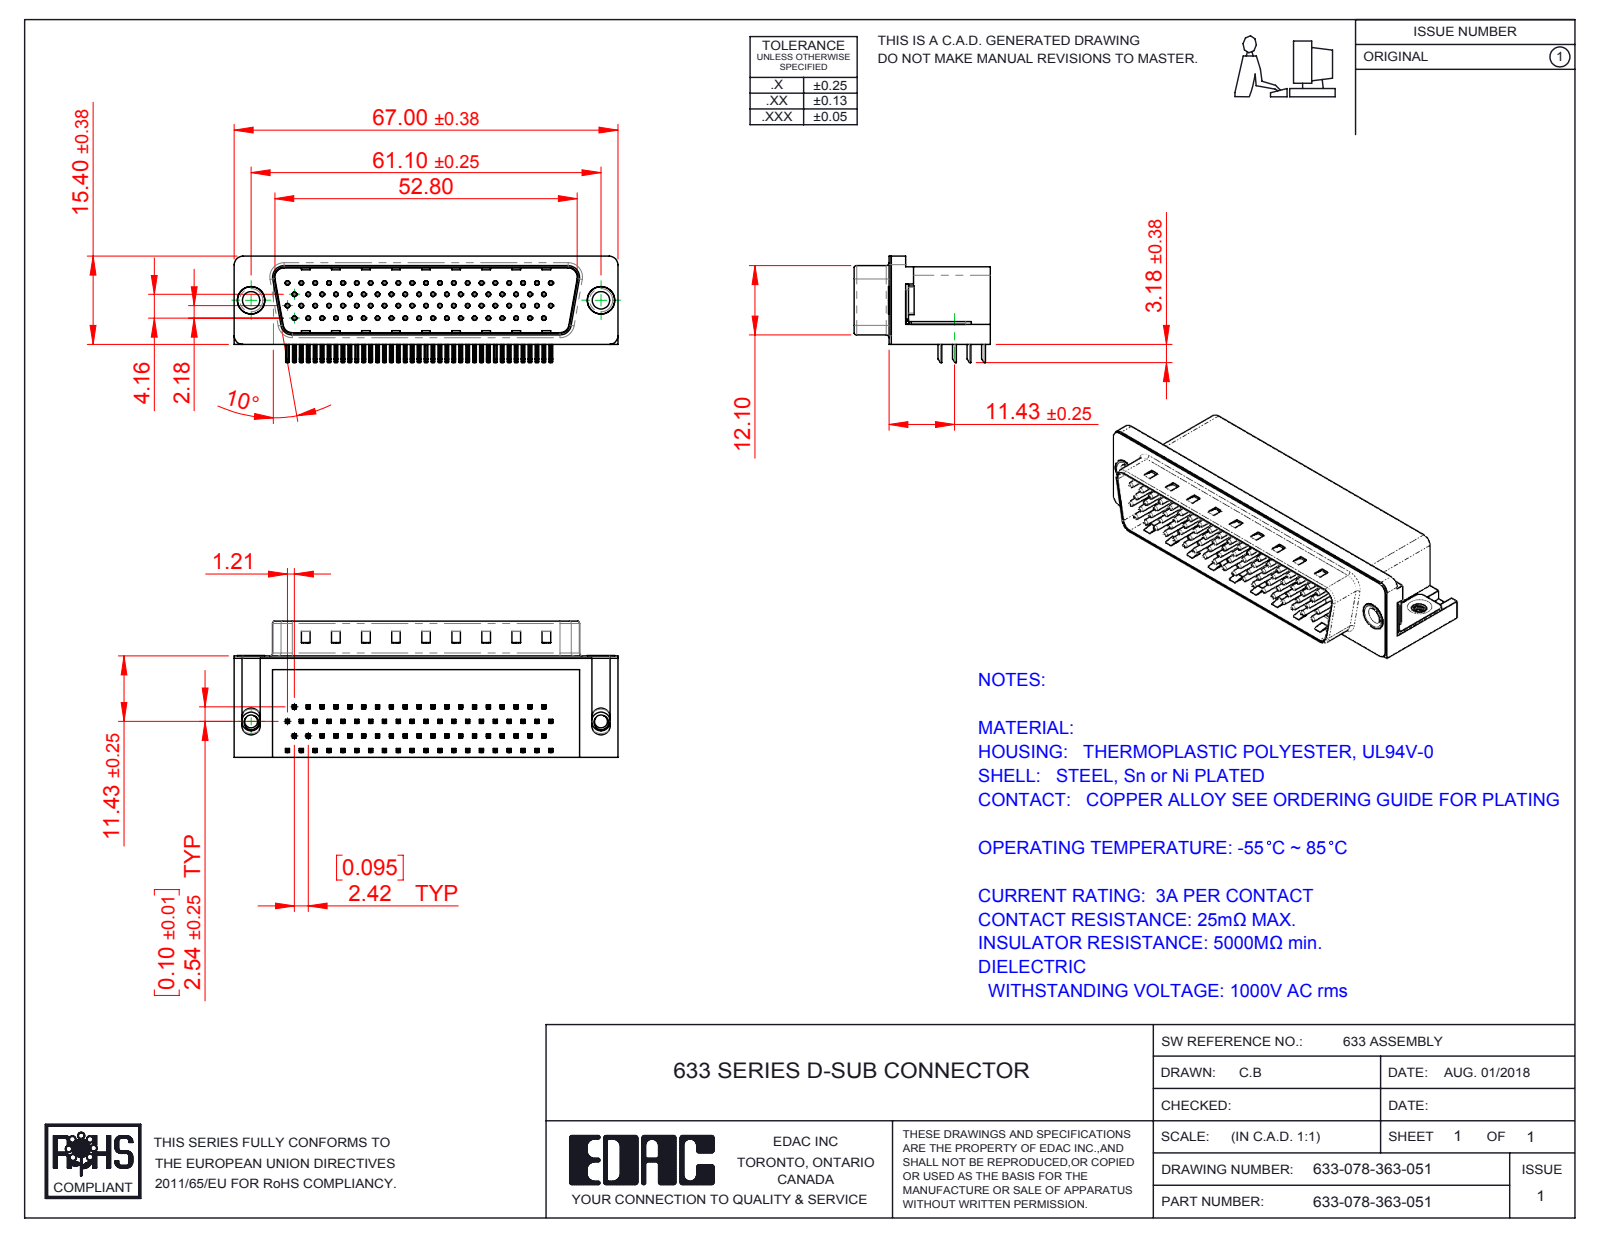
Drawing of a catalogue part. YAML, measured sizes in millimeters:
part_name: "633 4-40 Threaded Board Mount_78 Contact; 633 Contact Top_78 Contact; 633 Shell_78 Contact; 633 Thru Hole Rivet (+5 more)"
step_written_by: "SolidWorks 2016 (CONFIG_CONTROL_DESIGN)"
units: millimeters
bodies: {solids: 84, faces: 6266, planar: 3981, cylindrical: 1772, other: 513}
overall_size: [67, 23.8, 18.58]
volume: 14613
surface_area: 16409
round_holes:
  - {diameter: 0.35, count: 78}
  - {diameter: 0.8, count: 78}
  - {diameter: 2.26, count: 2}
  - {diameter: 3.05, count: 2}
  - {diameter: 4, count: 2}
  - {diameter: 4.8, count: 2}
  - {diameter: 5, count: 2}
round_bosses_or_shafts:
  - {diameter: 0.75, count: 78}
  - {diameter: 4.9, count: 2}
  - {diameter: 4.75, count: 2}
  - {diameter: 3.85, count: 2}
  - {diameter: 3.26, count: 2}
partial_cylinders:
  - {radius: 0.25, count: 320}
  - {radius: 0.12, count: 156}
  - {radius: 1, count: 16}
  - {radius: 0.5, count: 9}
  - {radius: 1.6, count: 8}
  - {radius: 1.5, count: 6}
  - {radius: 0.45, count: 4}
  - {radius: 0.9, count: 4}
face_to_face_distances: [0.4, 13.2, 17.3, 11.7, 13.35, 2.05, 13.75, 1.65, 1.85, 11.9]
hole_center_spacings: [2.42, 4.84, 7.26, 9.68, 6.26, 7.13, 12.1, 8.62]
